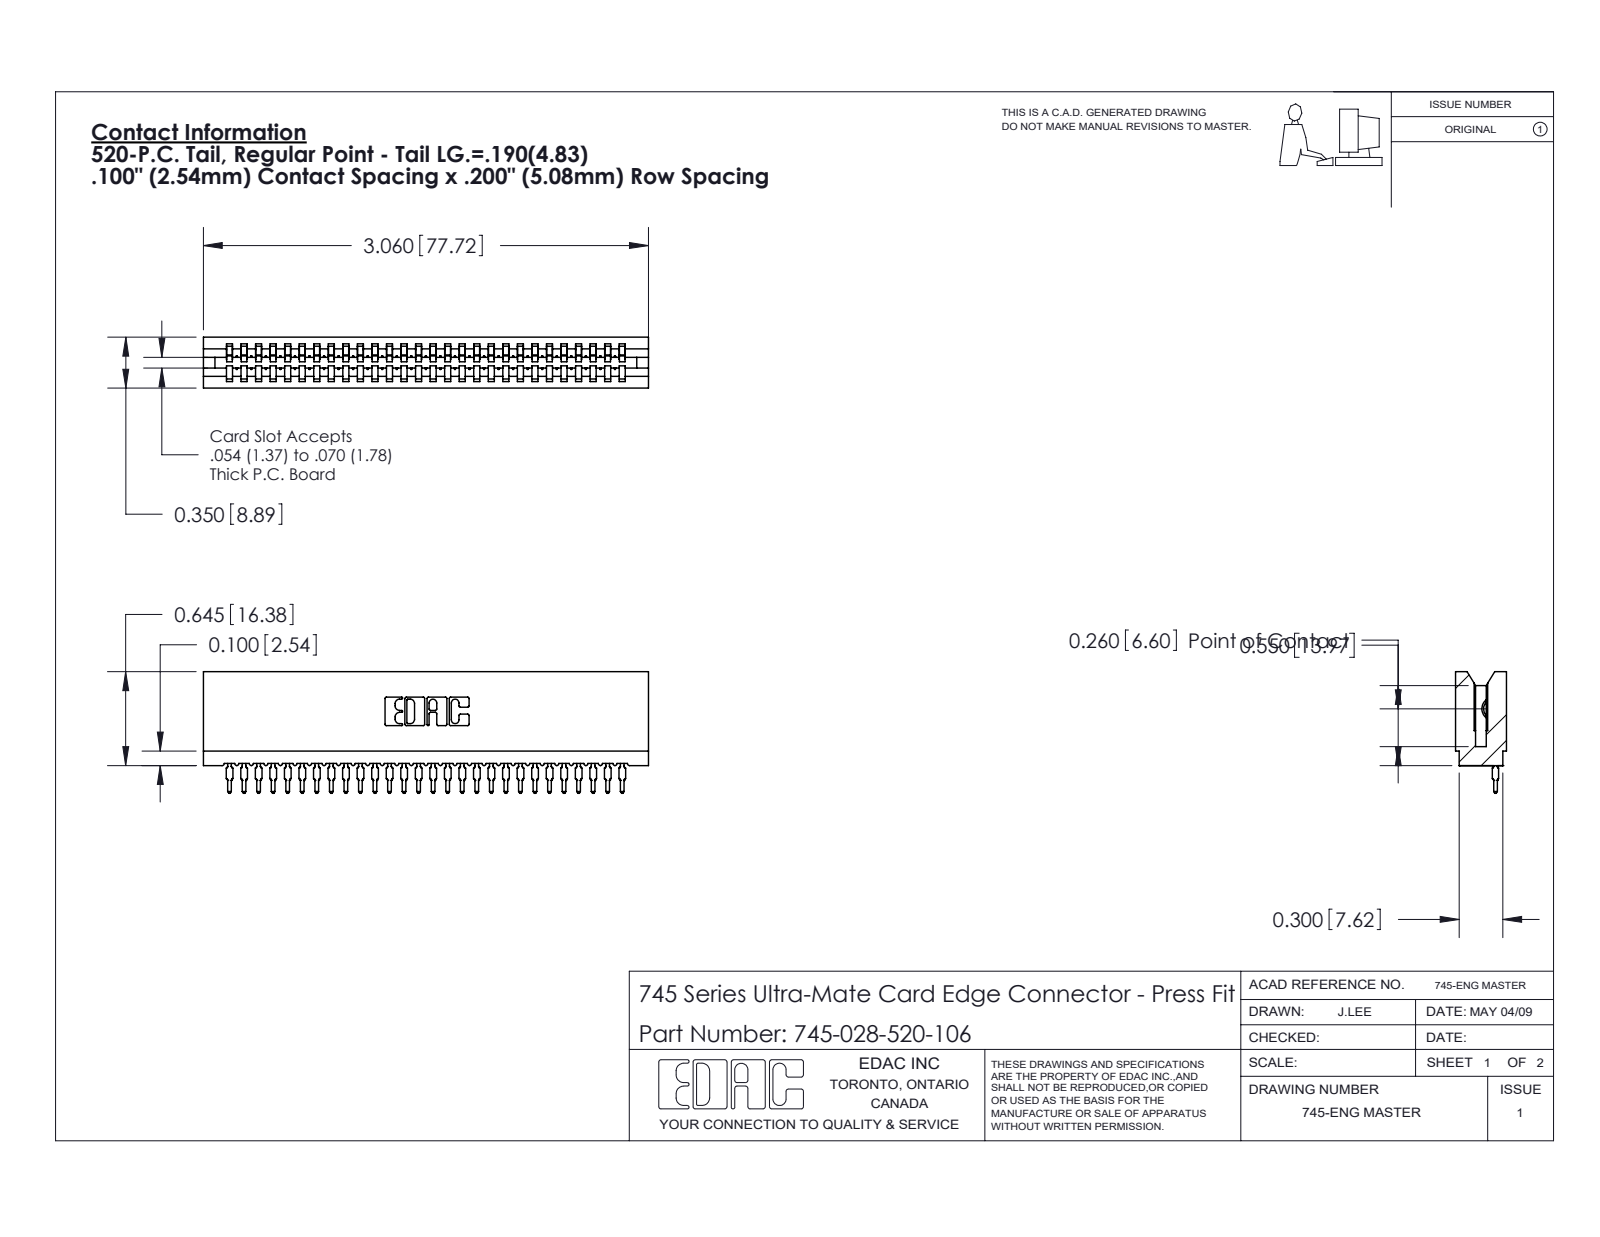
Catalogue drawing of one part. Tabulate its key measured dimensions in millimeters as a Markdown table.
| quantity | value |
| --- | --- |
| part name | 745-028-520-106; 745 Part_Insulator Option - 06; 745-292-001_520 |
| STEP written by | SolidWorks 2020 (CONFIG_CONTROL_DESIGN) |
| units | millimeters |
| bodies | 29 solids, 3232 faces (1932 planar, 572 cylindrical, 728 other) |
| overall size | 77.7 × 21.2 × 8.9 |
| volume | 6 770 mm³ |
| surface area | 12 190 mm² |
| partial cylindrical surfaces (radius × count) | 0.4 × 56, 0.5 × 56, 0.3 × 22, 0.2 × 6, 0.8 × 6, 0.1 × 4, 0.3 × 4, 0.7 × 3 |
| main face-to-face distances | 2.5, 8.9, 5.1, 3.5, 5.4, 1.1, 7.7, 2.4, 4.2, 7.6 |
